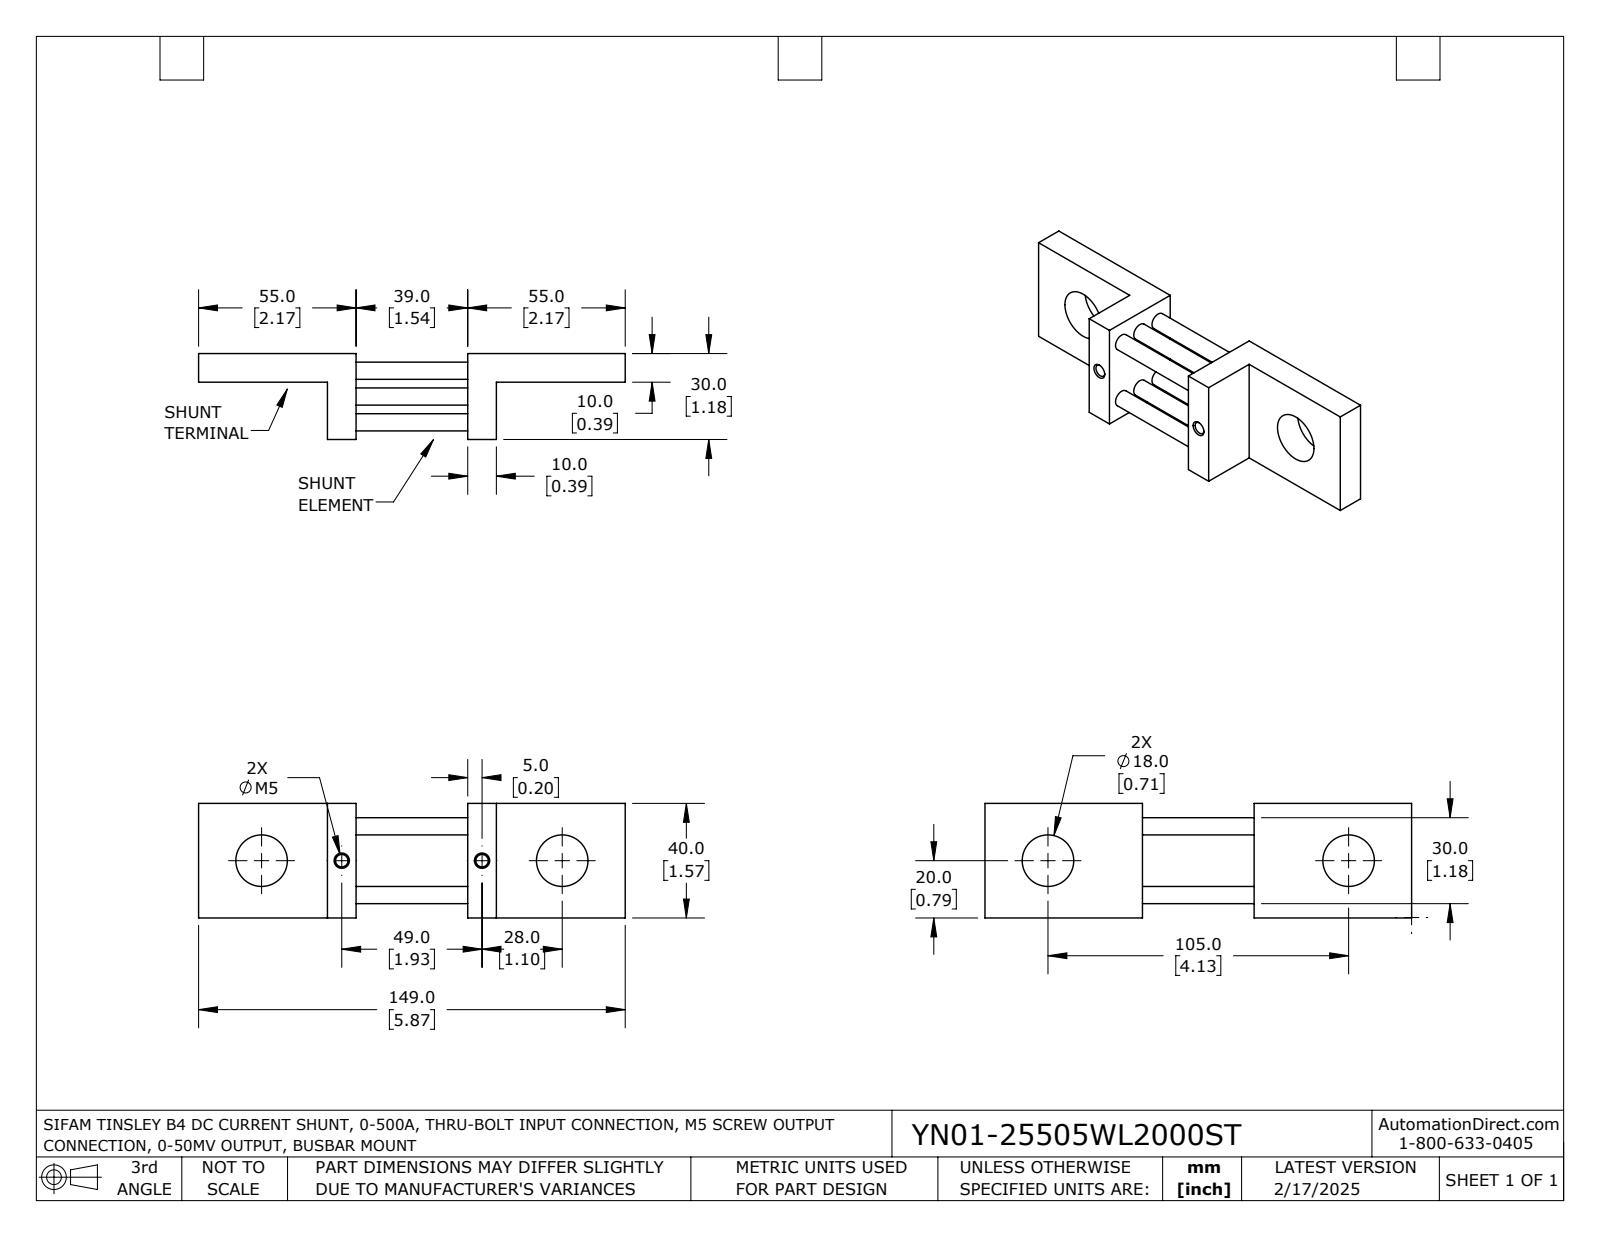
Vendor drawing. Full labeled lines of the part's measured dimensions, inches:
Part name (STEP PRODUCT): YN01-25505WL2000ST
STEP written by: SolidWorks 2021 (AUTOMOTIVE_DESIGN)
Units: inches
Bodies: 1 solid, 92 faces (40 planar, 44 cylindrical, 8 other)
Overall size (bounding box): 5.866 × 1.575 × 1.181
Volume: 3.731 in³ · Surface area: 33.76 in²
Round holes (diameter × count): ⌀0.236 ×6, ⌀0.171 ×2, ⌀0.709 ×2
Main face-to-face distances: 0.394, 1.929, 1.575, 1.535, 1.772, 2.165, 3.701, 4.094, 2.323, 1.181
Hole centre spacings: 0.354, 1.009, 0.945, 0.709, 1.102, 1.181, 3.031, 1.929
